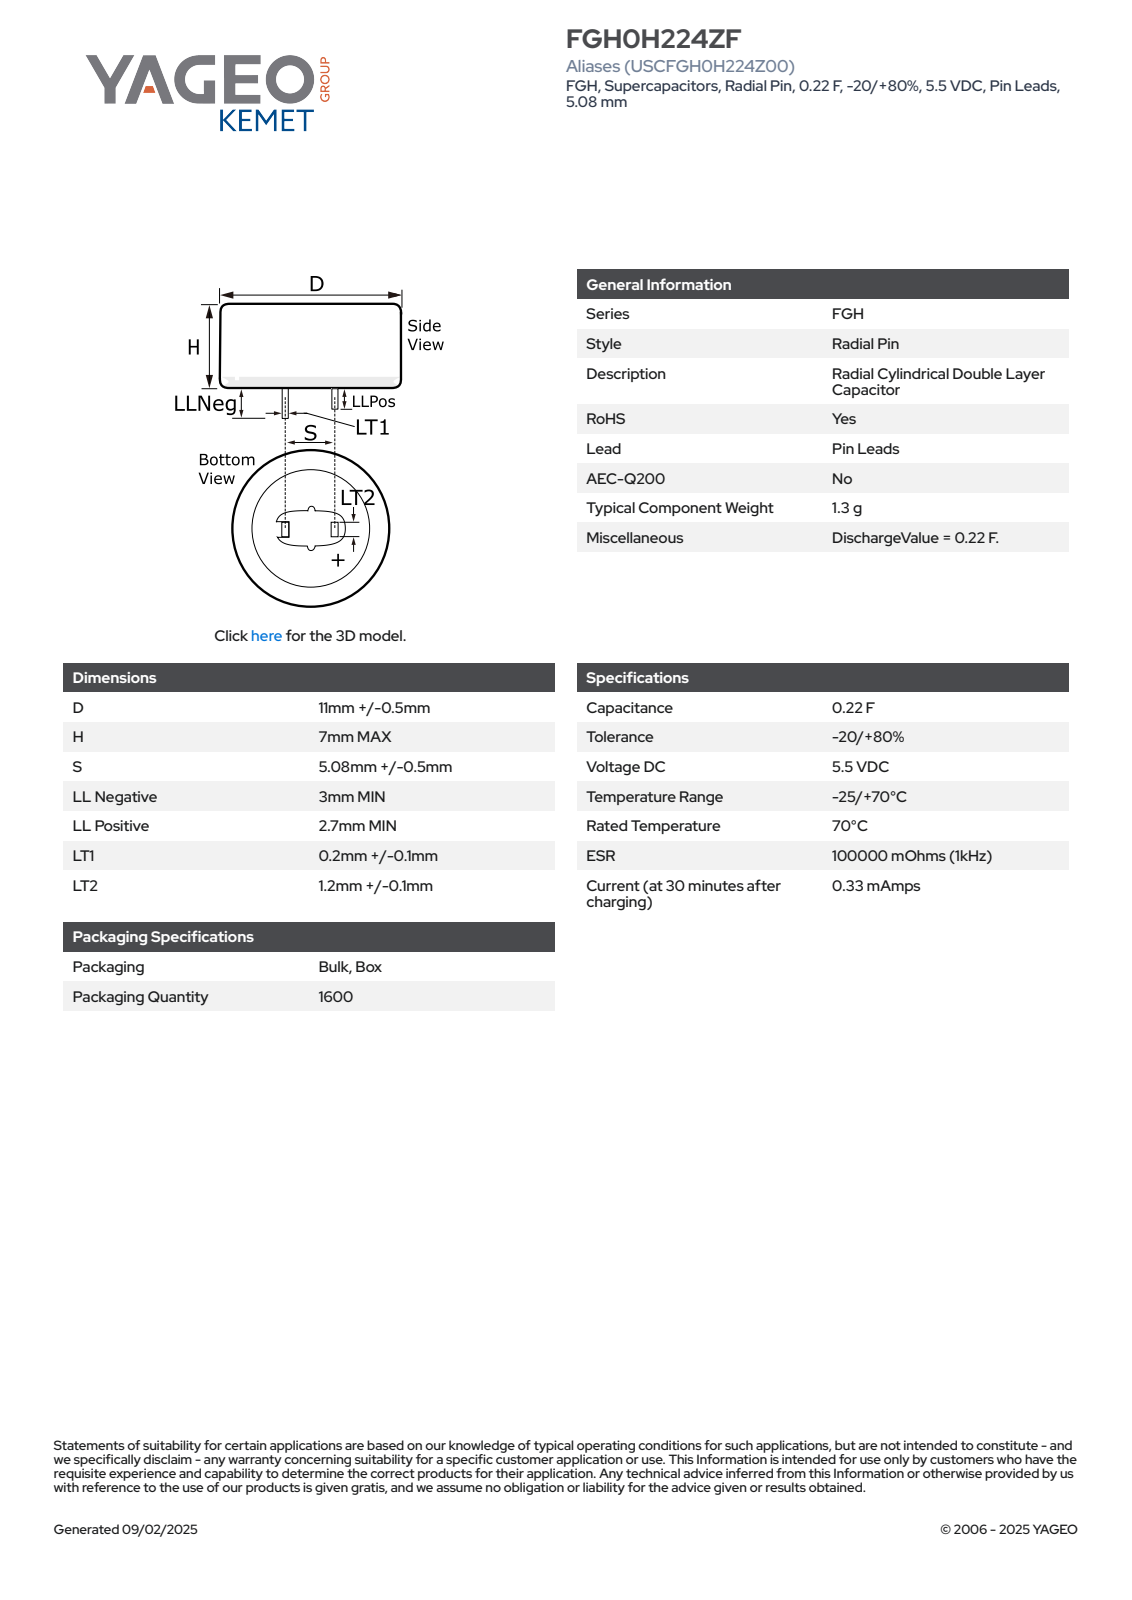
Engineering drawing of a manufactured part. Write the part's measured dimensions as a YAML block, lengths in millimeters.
part_name: "CDR_LPLLN_D11.5L7S5.08LLNEG3LLPOS2.7LT10.3LT21.3"
step_written_by: "SolidWorks 2014 (AUTOMOTIVE_DESIGN)"
units: millimeters
bodies: {solids: 1, faces: 78, planar: 70, cylindrical: 4, other: 4}
overall_size: [11.5, 11.5, 10]
volume: 726
surface_area: 465
round_bosses_or_shafts:
  - {diameter: 11.5, count: 1}
partial_cylinders:
  - {radius: 5.76, count: 1}
face_to_face_distances: [7, 5.08, 5.38, 4.78, 1.3, 2.7, 9.7, 3, 10, 0.45]
